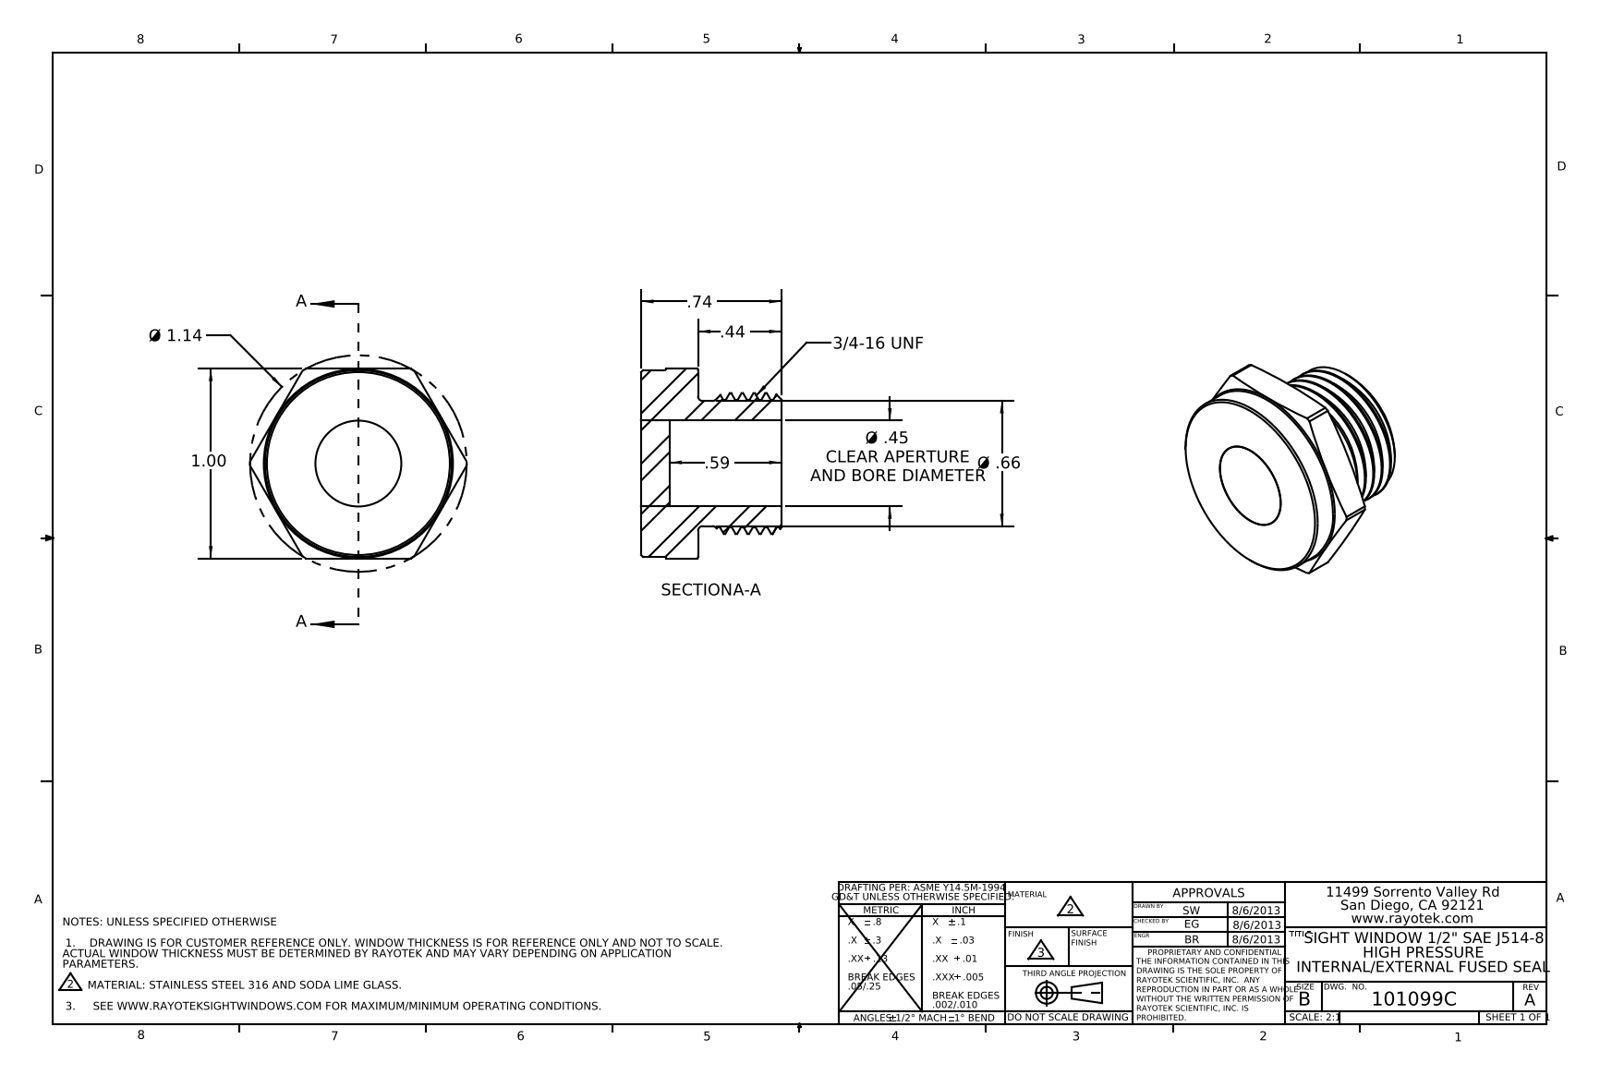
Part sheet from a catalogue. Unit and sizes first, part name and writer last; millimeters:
Units: millimetres
Overall size (bounding box): 29 × 25.4 × 18.8
Round holes (diameter × count): ⌀11.5 ×1
Round bosses / shafts (diameter × count): ⌀25 ×1, ⌀18.9 ×1, ⌀16.8 ×1
Partial cylindrical surfaces — rounded edges, fillets, slot ends (radius × count): R14.5 ×1
Main face-to-face distances: 7.6, 3.8, 25.4, 11.2, 18.8, 15
Volume: 5 190 mm³ · Surface area: 3 441 mm²
Bodies: 2 solids, 58 faces (11 planar, 26 cylindrical, 21 other)
Part name (STEP PRODUCT): 403099
STEP written by: SolidWorks 2012 (AUTOMOTIVE_DESIGN)
